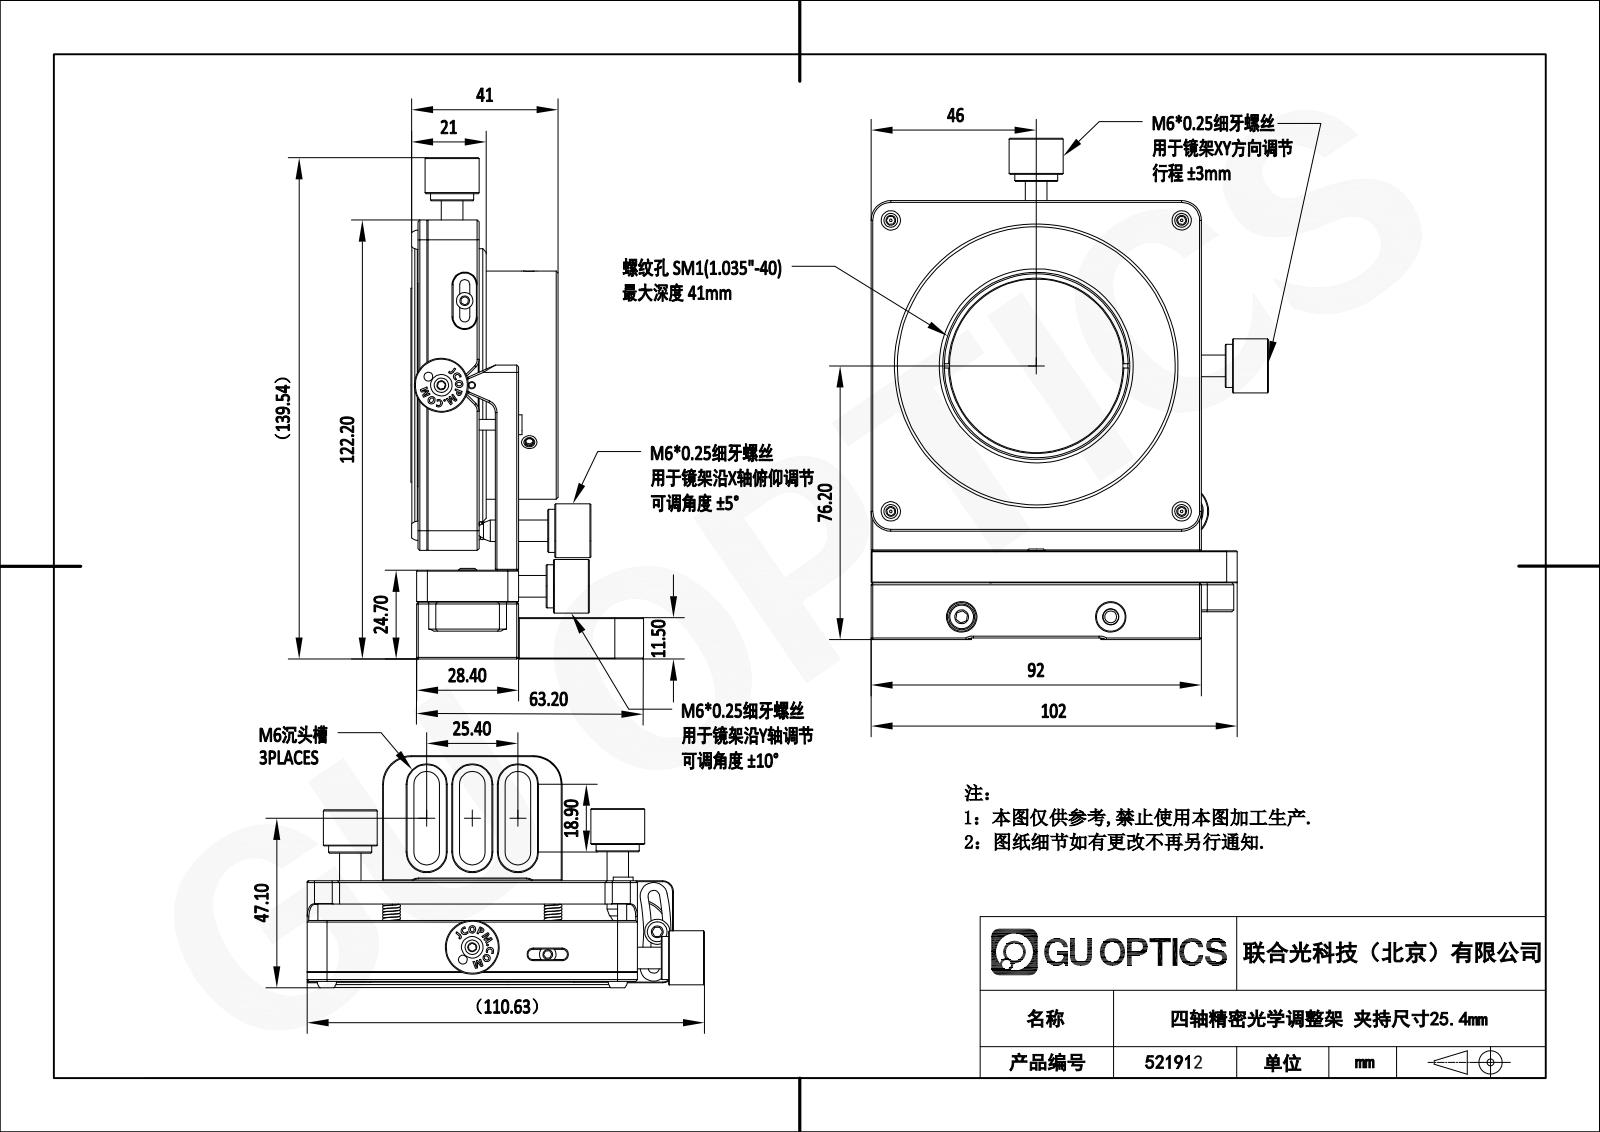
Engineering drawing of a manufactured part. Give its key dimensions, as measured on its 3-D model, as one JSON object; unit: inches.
{"part_name": "1.1.10.15_ZJP-Z4SM1", "step_written_by": "SolidWorks 2021 (CONFIG_CONTROL_DESIGN)", "units": "inches", "bodies": {"solids": 21, "faces": 1360, "planar": 515, "cylindrical": 364, "other": 481}, "overall_size": [5.328, 4.077, 2.551], "volume_in3": 15.55, "surface_area_in2": 104.5, "round_holes": [[0.098, 10], [0.039, 8], [0.13, 5], [0.236, 5], [0.134, 4], [0.148, 3], [0.217, 3], [0.126, 2], [0.138, 2], [0.157, 2], [0.177, 2], [0.197, 2]], "round_bosses_or_shafts": [[0.157, 7], [0.118, 7], [0.394, 5], [0.197, 5], [0.472, 4], [0.268, 4], [0.217, 2], [0.059, 2]], "partial_cylinders_radius": [[0.079, 7], [0.118, 7], [0.14, 6], [0.197, 6], [0.215, 6], [0.11, 5], [0.031, 4], [0.128, 4]], "face_to_face_distances": [0.079, 0.748, 0.433, 1.102, 0.669, 1.169, 0.354, 0.736, 3.622, 0.815], "hole_center_spacings": [0.102, 3.189, 0.205, 0.709, 1.102, 0.435, 0.492, 0.52]}
